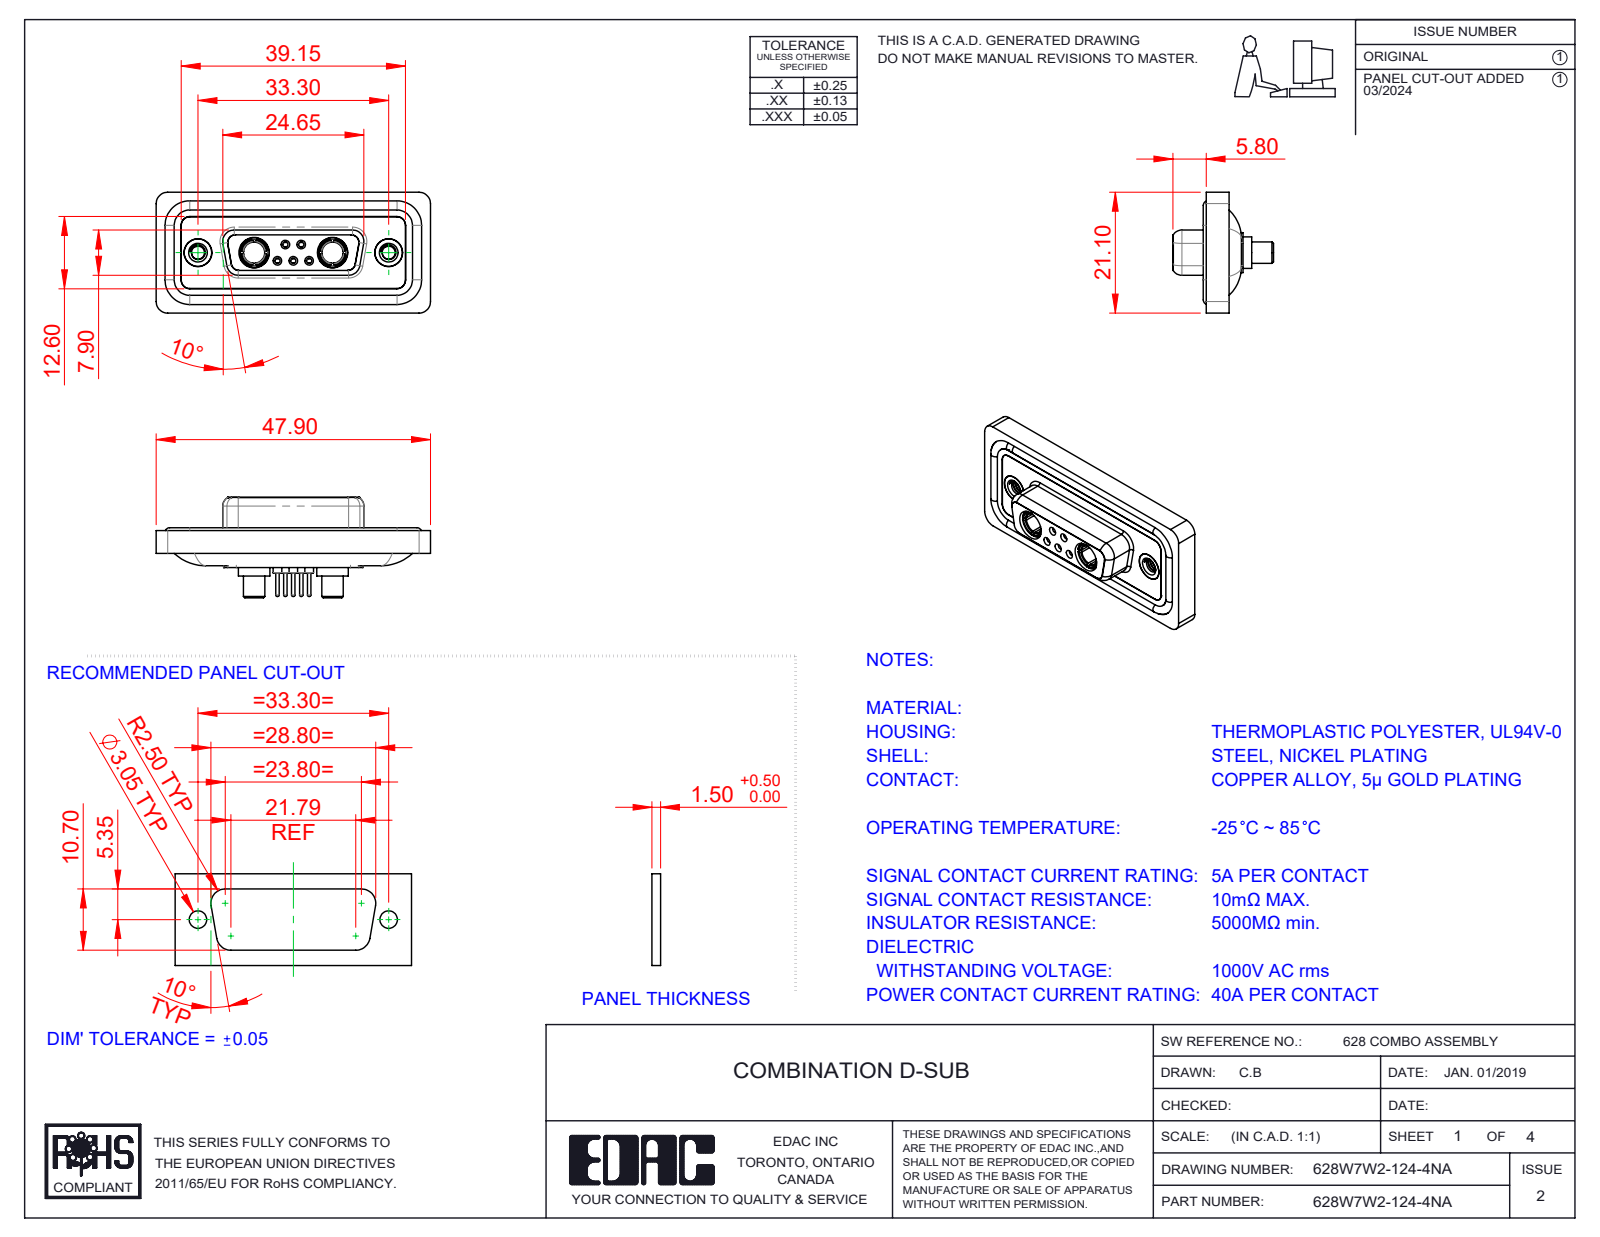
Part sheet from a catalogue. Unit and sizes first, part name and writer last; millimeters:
Units: millimetres
Overall size (bounding box): 47.9 × 21.1 × 17.55
Round holes (diameter × count): ⌀0.9 ×5, ⌀1.1 ×5, ⌀1.5 ×5, ⌀2 ×5, ⌀4.85 ×4, ⌀1.6 ×3, ⌀1.7 ×2, ⌀2.26 ×2, ⌀3.7 ×2, ⌀4 ×2, ⌀4.05 ×2, ⌀5 ×2
Round bosses / shafts (diameter × count): ⌀1.6 ×6, ⌀2.2 ×5, ⌀0.6 ×5, ⌀5.5 ×2, ⌀5.2 ×2, ⌀4.96 ×2, ⌀4.95 ×2, ⌀4.8 ×2
Partial cylindrical surfaces — rounded edges, fillets, slot ends (radius × count): R1.5 ×22, R2 ×20, R1.35 ×12, R1.6 ×8, R0.25 ×4, R0.5 ×4, R0.6 ×4, R0.65 ×4
Main face-to-face distances: 0.4, 1.8, 1.6, 0.5, 2.9, 7.45, 1.1, 5.65, 6.6, 7.05
Hole centre spacings: 3.16, 2.77, 9.8, 23.5, 4.31, 4.33, 5.03, 5.04
Volume: 6 116 mm³ · Surface area: 9 904 mm²
Bodies: 16 solids, 807 faces (238 planar, 331 cylindrical, 238 other)
Part name (STEP PRODUCT): 628Combo Shell Front_15 Contacts; Power Socket_40A S; 628Combo Contact Row 1_24; 628Combo Contact Row 2_24 (+5 more)
STEP written by: SolidWorks 2023 (CONFIG_CONTROL_DESIGN)
